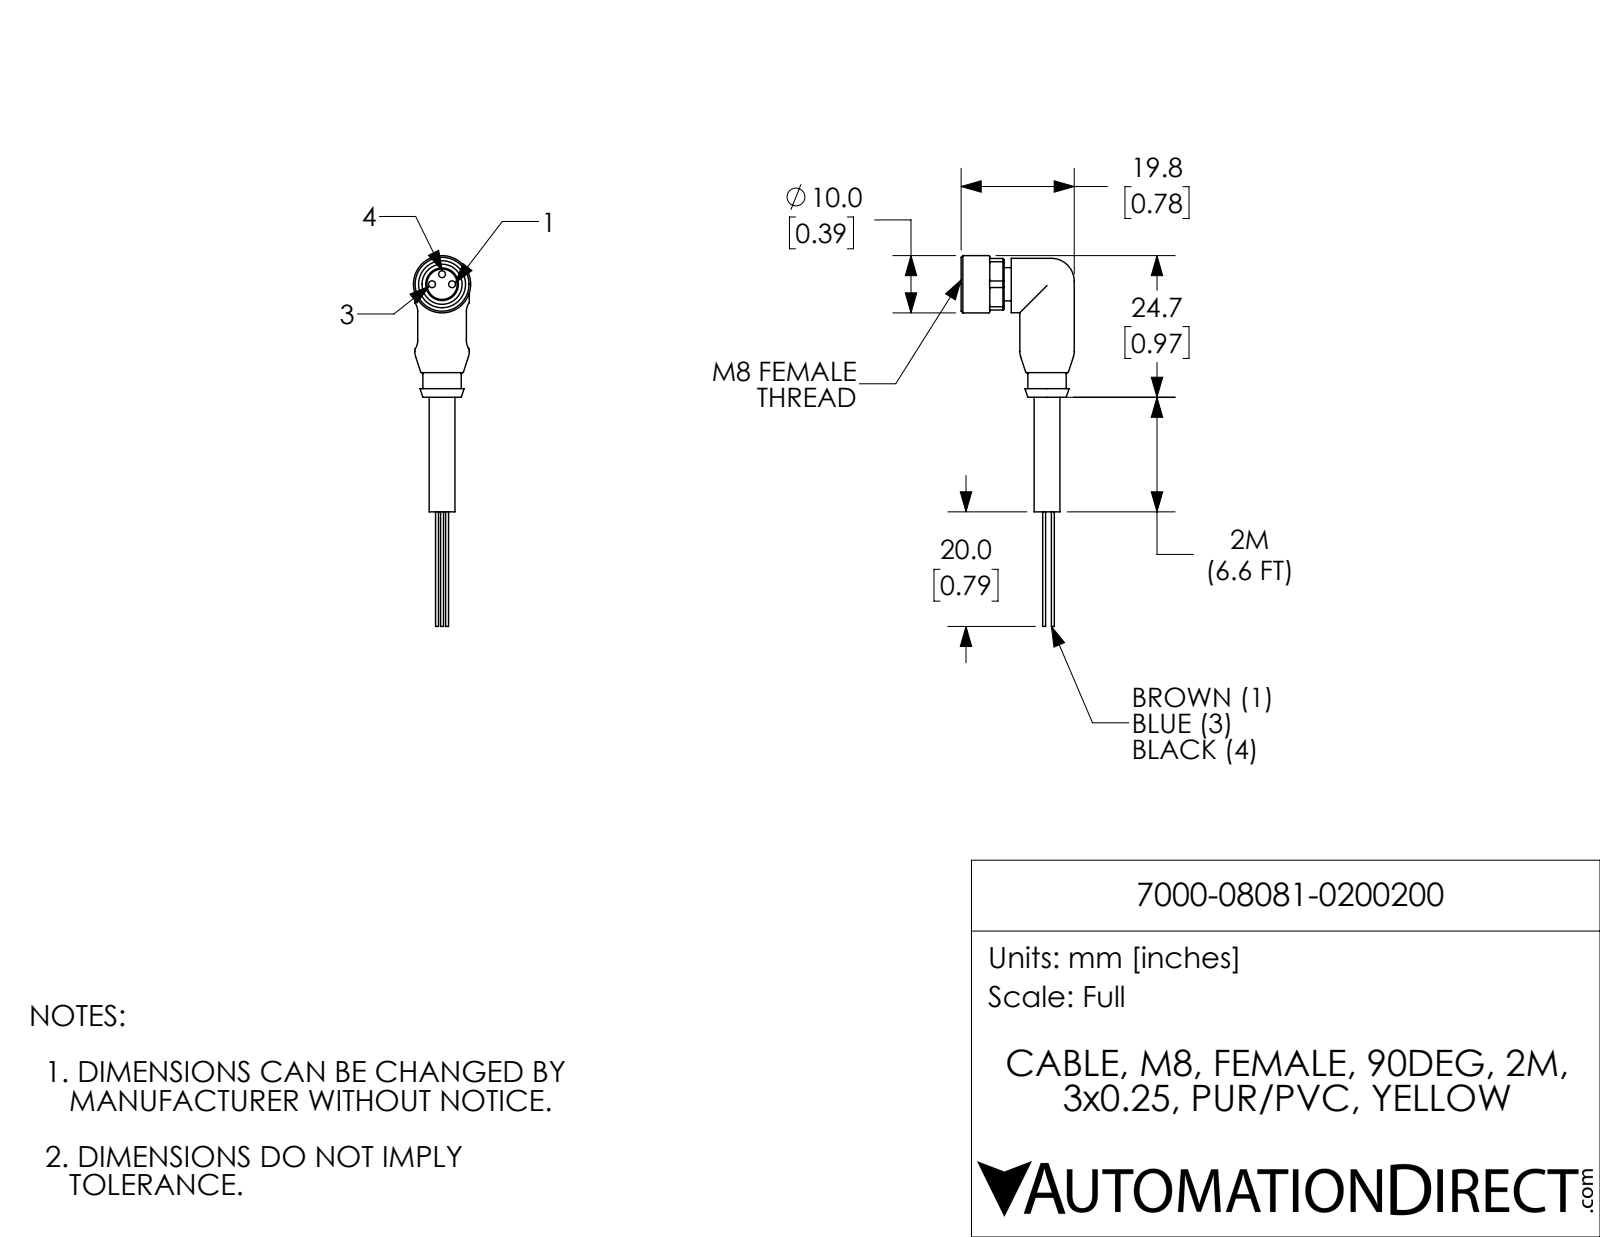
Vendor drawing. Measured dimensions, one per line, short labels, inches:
name: 7000-08081-0200200
written by: SolidWorks 2017 (AUTOMOTIVE_DESIGN)
unit: in
bodies: 1 solid, 107 faces (35 planar, 43 cylindrical, 29 other)
size: 2.548 × 0.778 × 0.394
volume: 0.147 in³; area: 2.844 in²
holes: 3× ⌀0.047, 1× ⌀0.276
bosses: 3× ⌀0.02, 2× ⌀0.374, 1× ⌀0.394, 1× ⌀0.264, 1× ⌀0.228, 1× ⌀0.224, 1× ⌀0.177
rounds: 4× R0.008, 4× R0.098, 1× R0.193
face distances: 0.049, 0.354, 0.059, 0.335, 0.028, 0.268, 0.317, 0.295, 0.344, 0.787
hole spacings: 0.069, 0.097, 0.138
